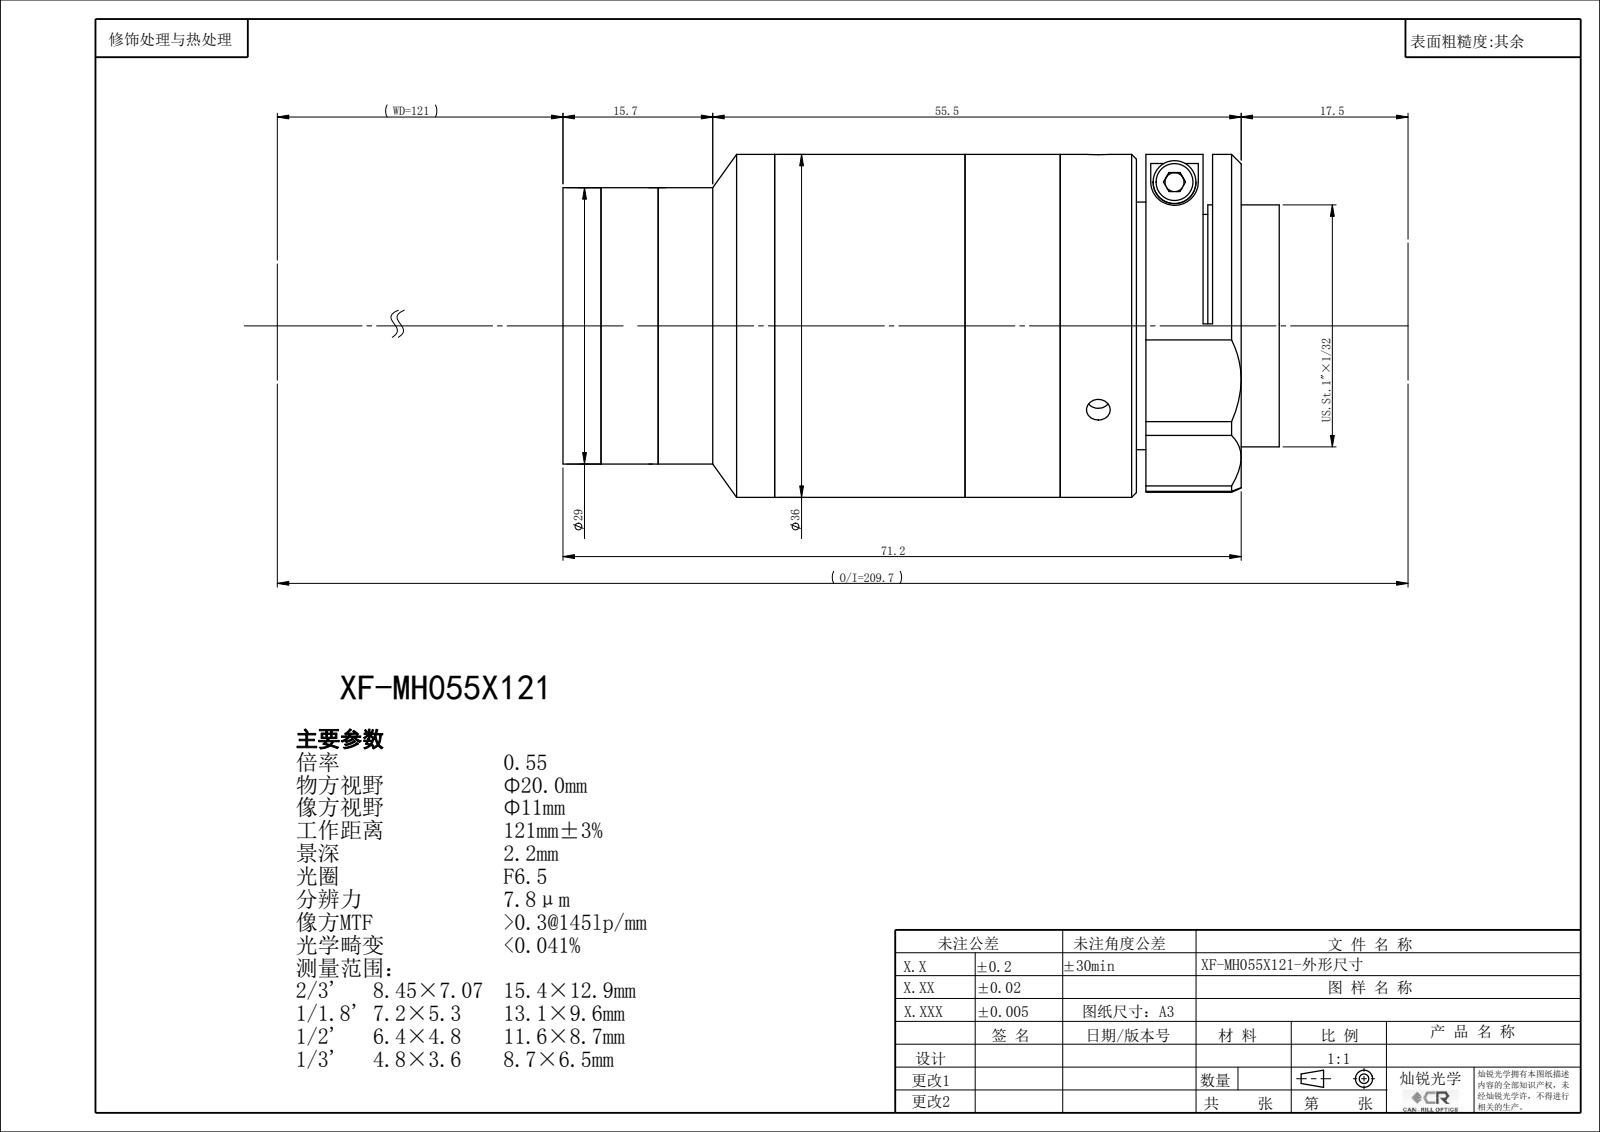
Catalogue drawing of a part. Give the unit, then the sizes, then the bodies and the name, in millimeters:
Units: millimetres
Overall size (bounding box): 75.3 × 36.01 × 36
Round holes (diameter × count): ⌀2.5 ×3, ⌀14 ×1, ⌀22.4 ×1, ⌀24 ×1, ⌀24.9 ×1, ⌀26 ×1, ⌀26.4 ×1
Round bosses / shafts (diameter × count): ⌀36 ×1, ⌀34 ×1, ⌀29 ×1, ⌀25.4 ×1
Main face-to-face distances: 19.06, 48.44, 67.5, 1.5, 66, 17.56, 10, 38.44, 27.56, 29.06
Bodies: 0 solids, 131 faces (67 planar, 42 cylindrical, 22 other)
Part name (STEP PRODUCT): XF-MH055X121
STEP written by: SolidWorks 2022 (CONFIG_CONTROL_DESIGN)
